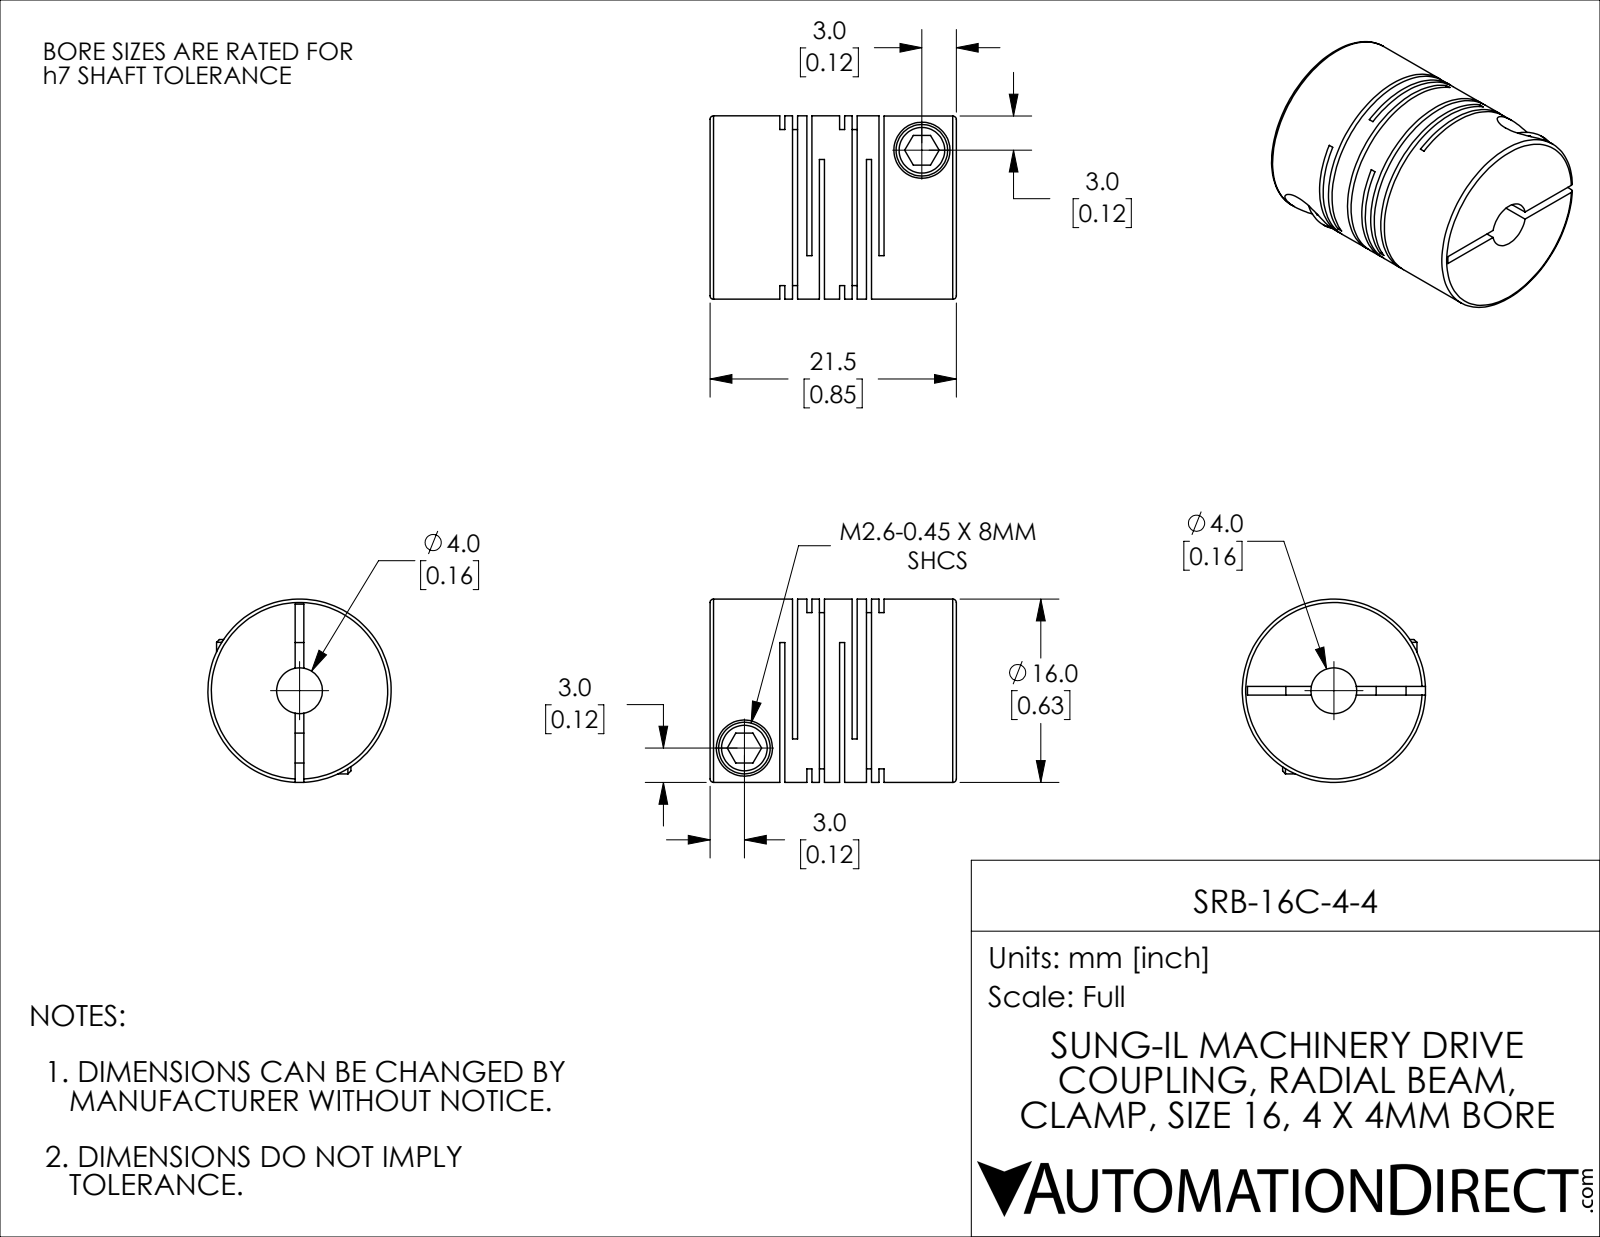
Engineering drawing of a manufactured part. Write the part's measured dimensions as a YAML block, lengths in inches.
part_name: "SRB-16C-4-4"
step_written_by: "SolidWorks 2021 (CONFIG_CONTROL_DESIGN)"
units: inches
bodies: {solids: 1, faces: 114, planar: 60, cylindrical: 42, other: 12}
overall_size: [0.846, 0.63, 0.63]
volume: 0.202
surface_area: 6.908
round_holes:
  - {diameter: 0.102, count: 2}
  - {diameter: 0.193, count: 2}
  - {diameter: 0.157, count: 1}
round_bosses_or_shafts:
  - {diameter: 0.177, count: 2}
  - {diameter: 0.63, count: 1}
face_to_face_distances: [0.205, 0.017, 0.043, 0.093, 0.026, 0.075, 0.188, 0.049, 0.162, 0.113]
